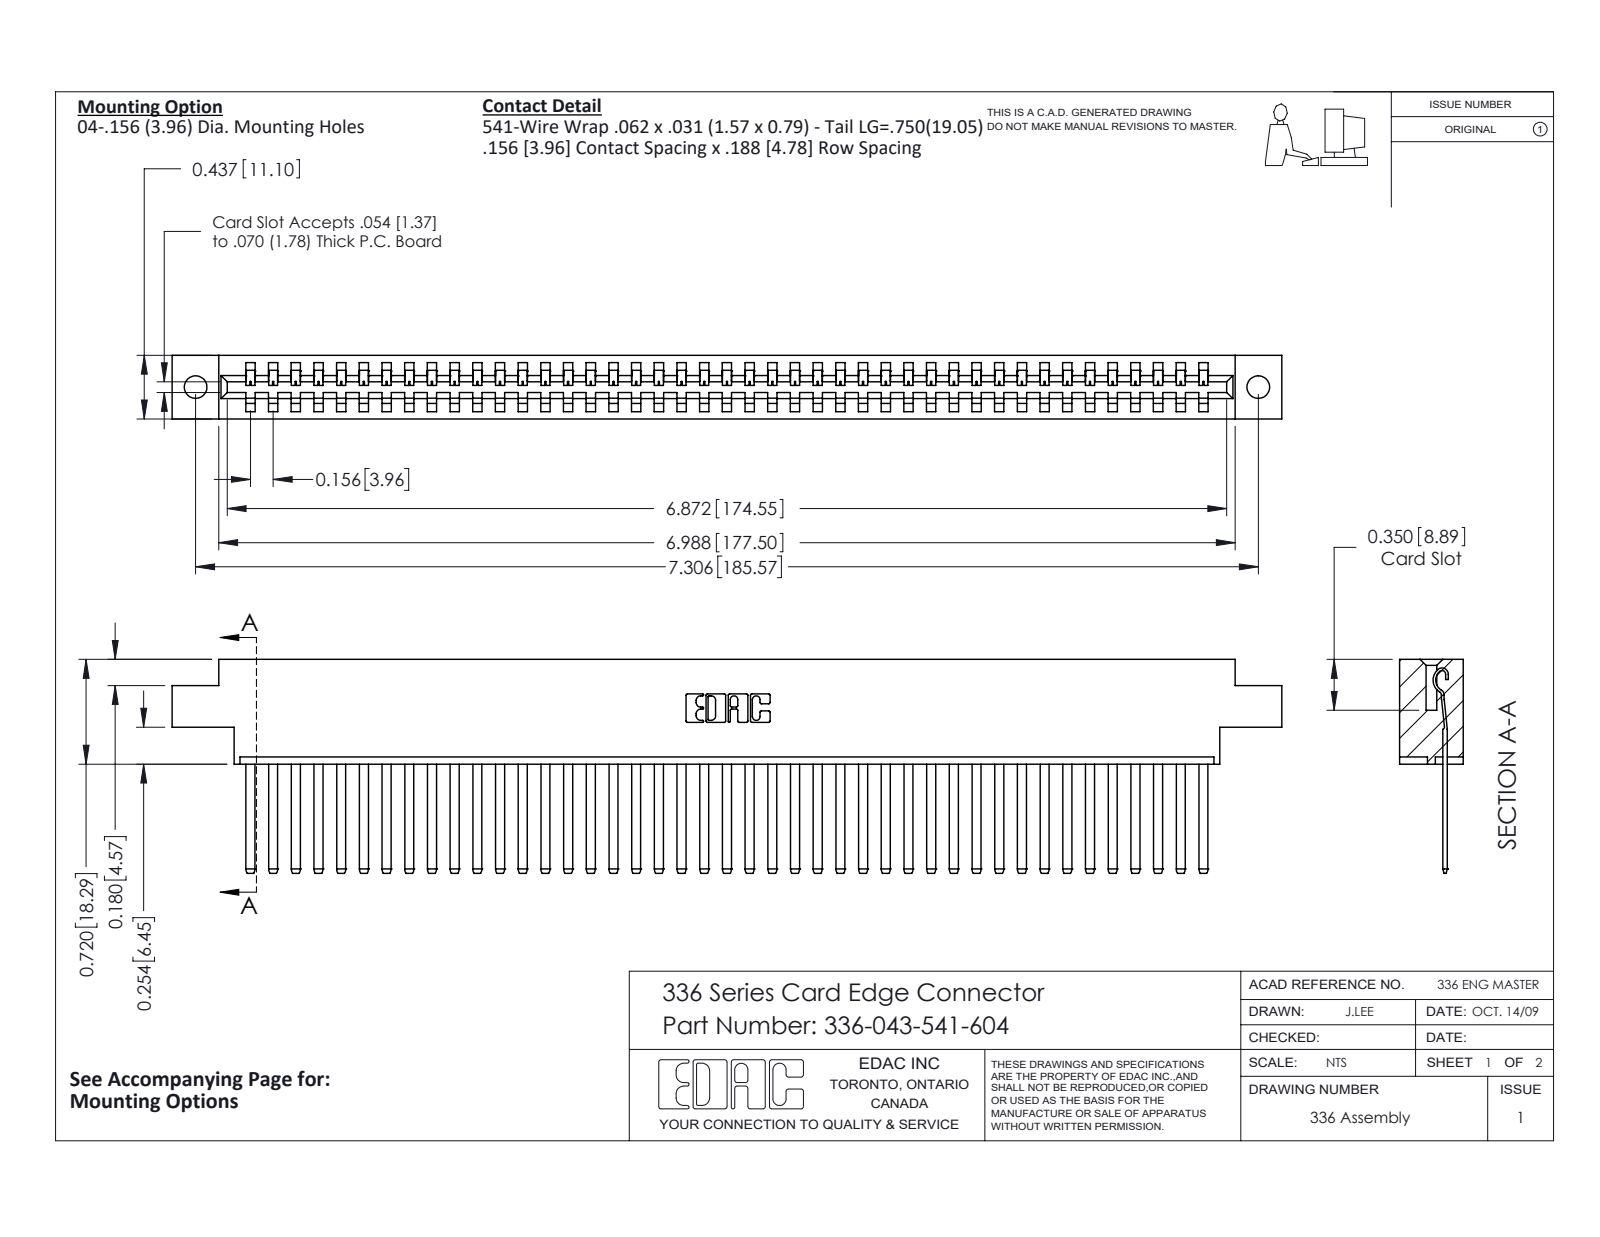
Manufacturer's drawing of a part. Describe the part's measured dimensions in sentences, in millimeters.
The part is named "336-043-541-604; 336 Part_Offset - .156 Dia - TH; 336-290-001_336-290-541". Its 3-D file was written by "SolidWorks 2020 (CONFIG_CONTROL_DESIGN)". It is 44 solids with 2268 faces: 1536 planar, 732 cylindrical and 0 other. Overall it measures 193.8 by 37.3 by 11.1 millimeters. Its volume is 28 170 cubic millimeters and its surface area 30 560 square millimeters. Round holes: 2 of diameter 4. Partial cylindrical surfaces (rounded edges, fillets, slot ends): 86 of radius 0.1, 86 of radius 1.4, 22 of radius 0.3, 6 of radius 0.2, 6 of radius 0.8, 3 of radius 0.7, 2 of radius 0.6, 2 of radius 1. The main face-to-face distances are 11.1, 4.6, 8.3, 3.6, 7.5, 2.8, 0.8, 6.5, 1.3, 9.8. The hole center spacings are 185.6.
